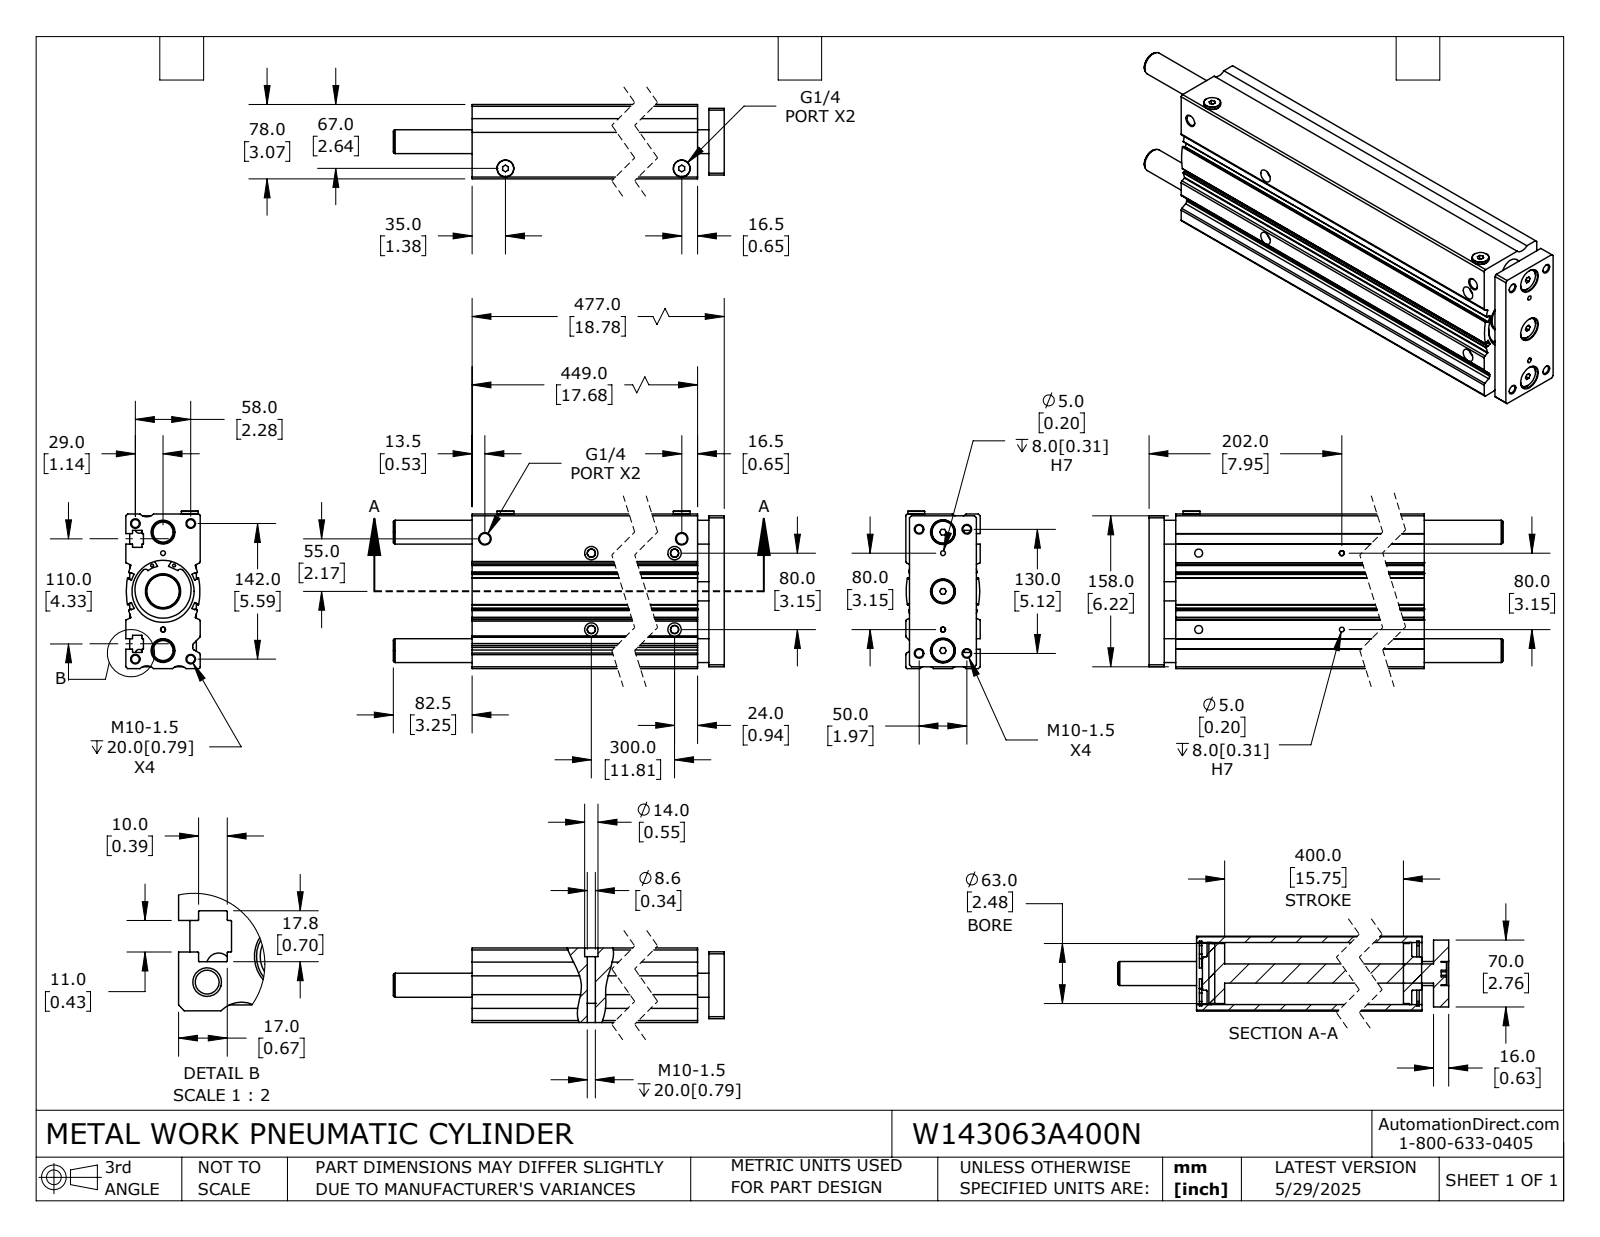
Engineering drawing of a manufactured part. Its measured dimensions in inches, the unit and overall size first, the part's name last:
Units: inches
Overall size (bounding box): 22.028 × 6.496 × 3.071
Round holes (diameter × count): ⌀0.33 ×12, ⌀0.118 ×4, ⌀0.197 ×4, ⌀0.339 ×4, ⌀0.551 ×4, ⌀0.984 ×3, ⌀0.448 ×2, ⌀2.559 ×1
Round bosses / shafts (diameter × count): ⌀0.945 ×3, ⌀0.697 ×2, ⌀2.677 ×1, ⌀2.551 ×1, ⌀2.48 ×1, ⌀1.378 ×1, ⌀0.787 ×1
Partial cylindrical surfaces — rounded edges, fillets, slot ends (radius × count): R0.012 ×44, R0.02 ×12, R0.079 ×8, R0.098 ×4, R0.118 ×4, R0.394 ×3, R0.124 ×2, R1.157 ×2
Main face-to-face distances: 3.071, 6.378, 4.331, 0.134, 0.567, 0.728, 2.343, 0.63, 0.673, 1.374
Hole centre spacings: 0.284, 0.682, 0.991, 1.158, 1.195, 1.392, 1.448, 1.585
Volume: 254.6 in³ · Surface area: 1 024 in²
Bodies: 6 solids, 454 faces (182 planar, 216 cylindrical, 56 other)
Part name (STEP PRODUCT): W143063A400N; W143063A400N_BODY; W143063A400N_ROD
STEP written by: SolidWorks 2024 (CONFIG_CONTROL_DESIGN)
